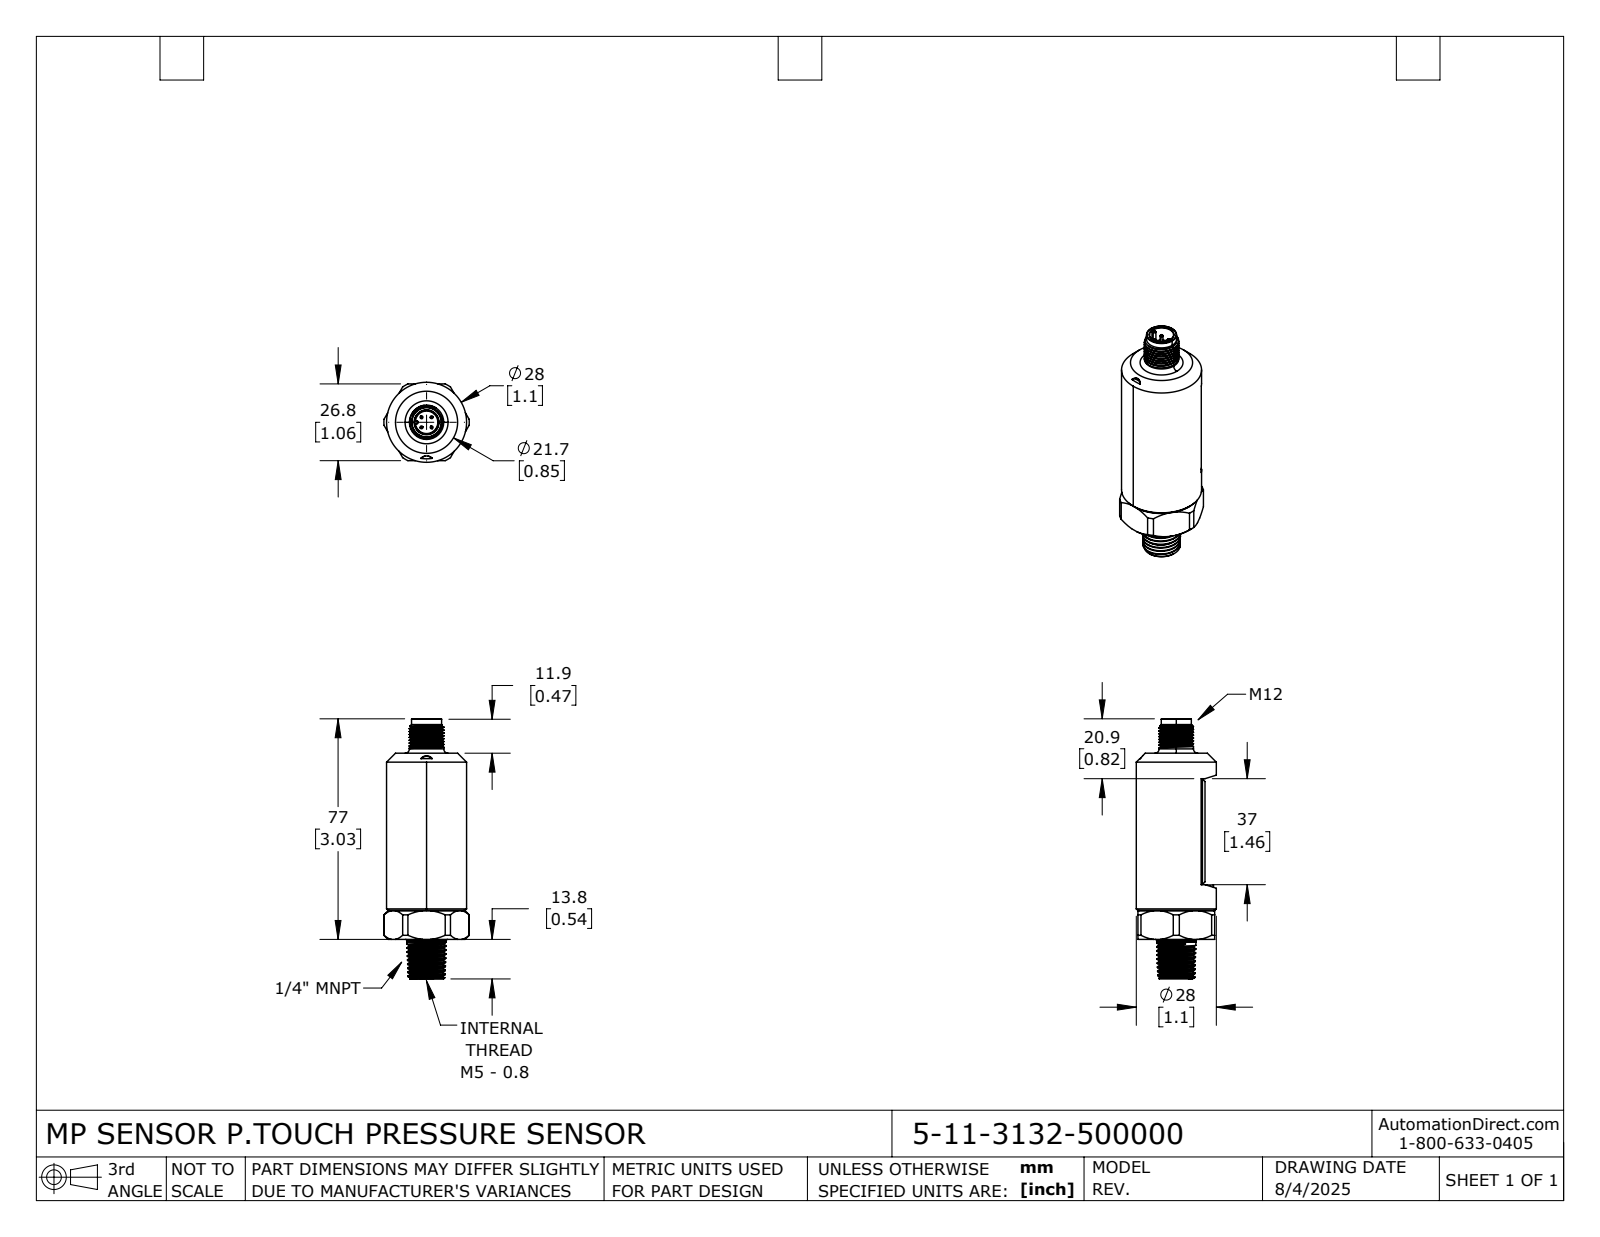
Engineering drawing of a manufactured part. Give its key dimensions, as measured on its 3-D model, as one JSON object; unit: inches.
{"part_name": "5-11-3132-500000", "step_written_by": "SolidWorks 2024 (AUTOMOTIVE_DESIGN)", "units": "inches", "bodies": {"solids": 1, "faces": 199, "planar": 46, "cylindrical": 68, "other": 85}, "overall_size": [3.575, 1.173, 1.1], "volume_in3": 2.423, "surface_area_in2": 13.82, "round_holes": [[0.079, 1], [0.165, 1], [0.331, 1]], "round_bosses_or_shafts": [[0.039, 4], [1.1, 1], [1.024, 1], [0.539, 1], [0.472, 1], [0.413, 1]], "partial_cylinders_radius": [[0.006, 2], [0.092, 1], [0.587, 1]], "face_to_face_distances": [1.055, 2.559, 0.922, 0.133, 0.543, 3.102, 0.354, 1.811, 0.35, 0.186]}
